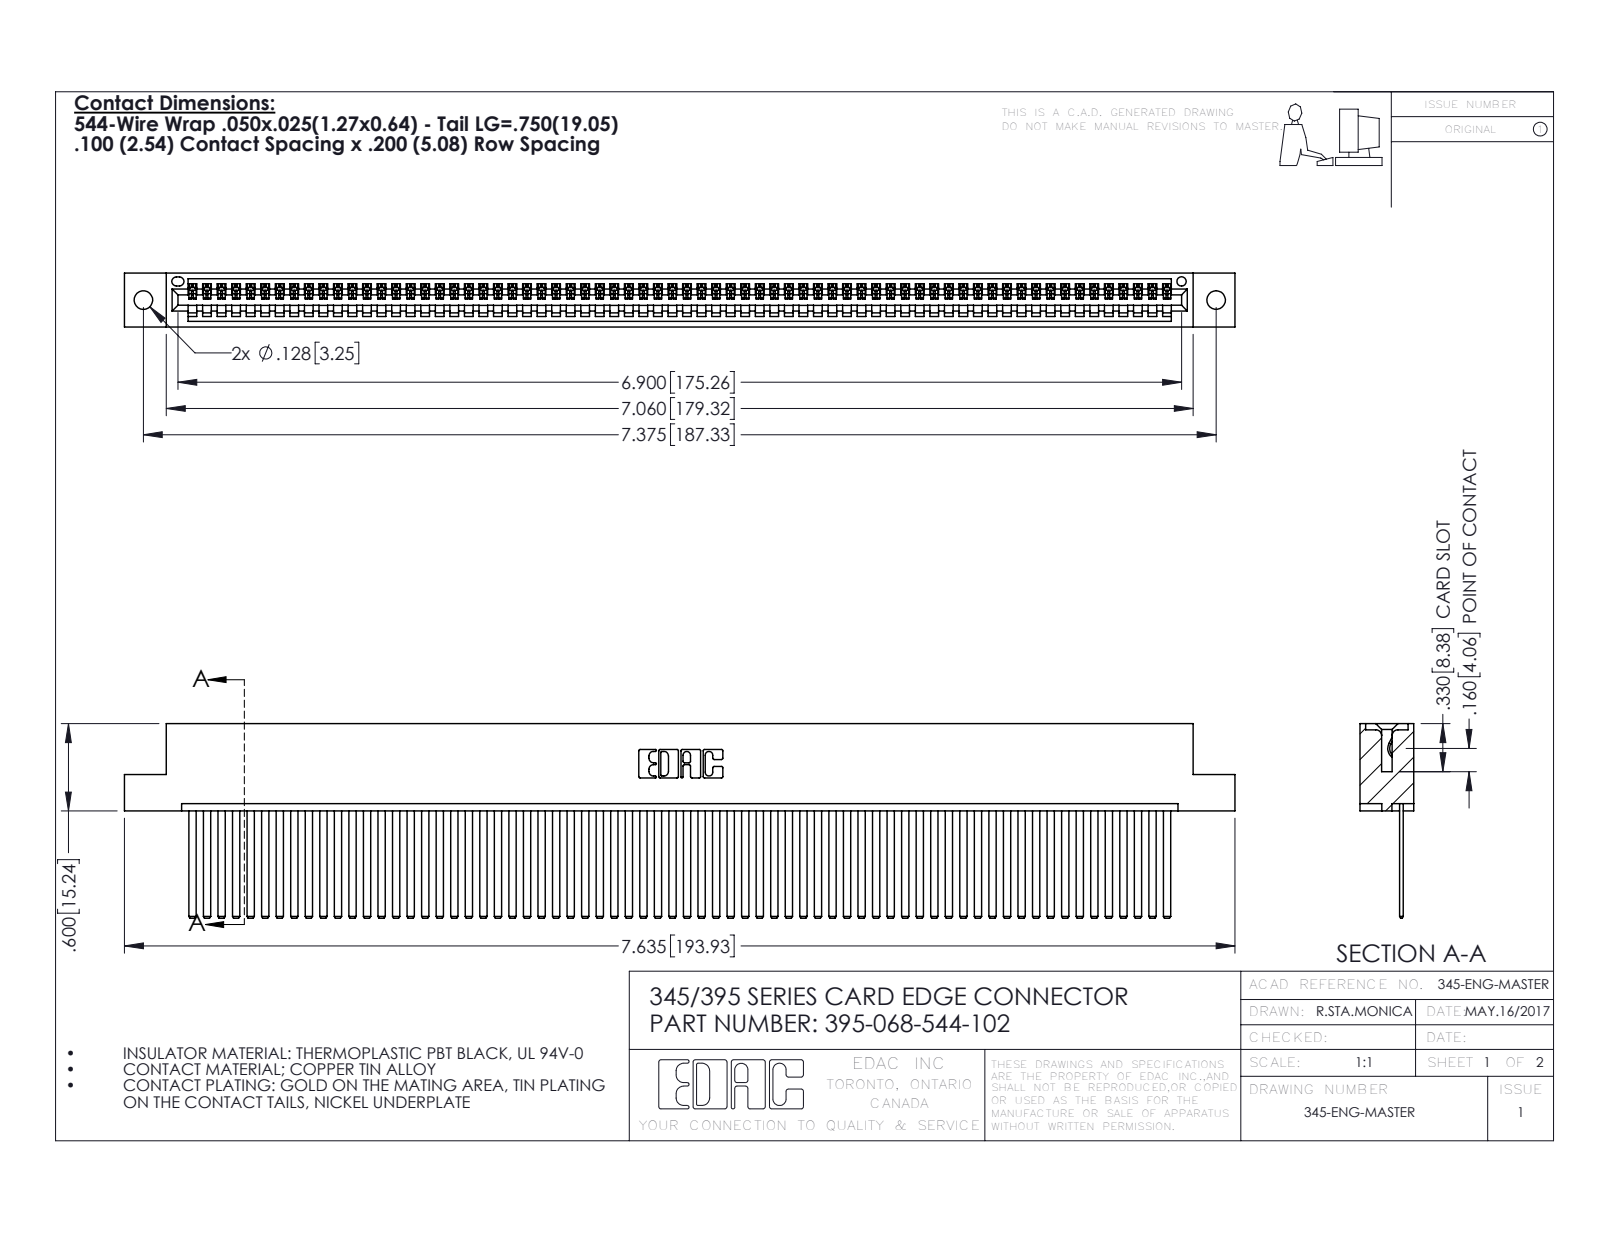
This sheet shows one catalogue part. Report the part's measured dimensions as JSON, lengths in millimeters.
{"part_name": "345-292-001_345-293-144; 345 Part_Flush Mounting Lugs - 0.128 Dia; 395-068-544-102", "step_written_by": "SolidWorks 2016 (CONFIG_CONTROL_DESIGN)", "units": "millimeters", "bodies": {"solids": 69, "faces": 3662, "planar": 2528, "cylindrical": 1134, "other": 0}, "overall_size": [193.9, 34, 9.4], "volume_mm3": 19390, "surface_area_mm2": 28210, "round_holes": [[3.3, 2], [1.6, 1]], "partial_cylinders_radius": [[0.2, 136], [0.3, 22], [0.2, 6], [0.8, 6], [0.7, 3], [0.8, 2], [1, 2], [0.4, 1]], "face_to_face_distances": [1.8, 7.6, 0.6, 2.5, 6.9, 9.4, 5.1, 5.7, 3.8, 1.8], "hole_center_spacings": [6.9, 181.3, 187.3]}
